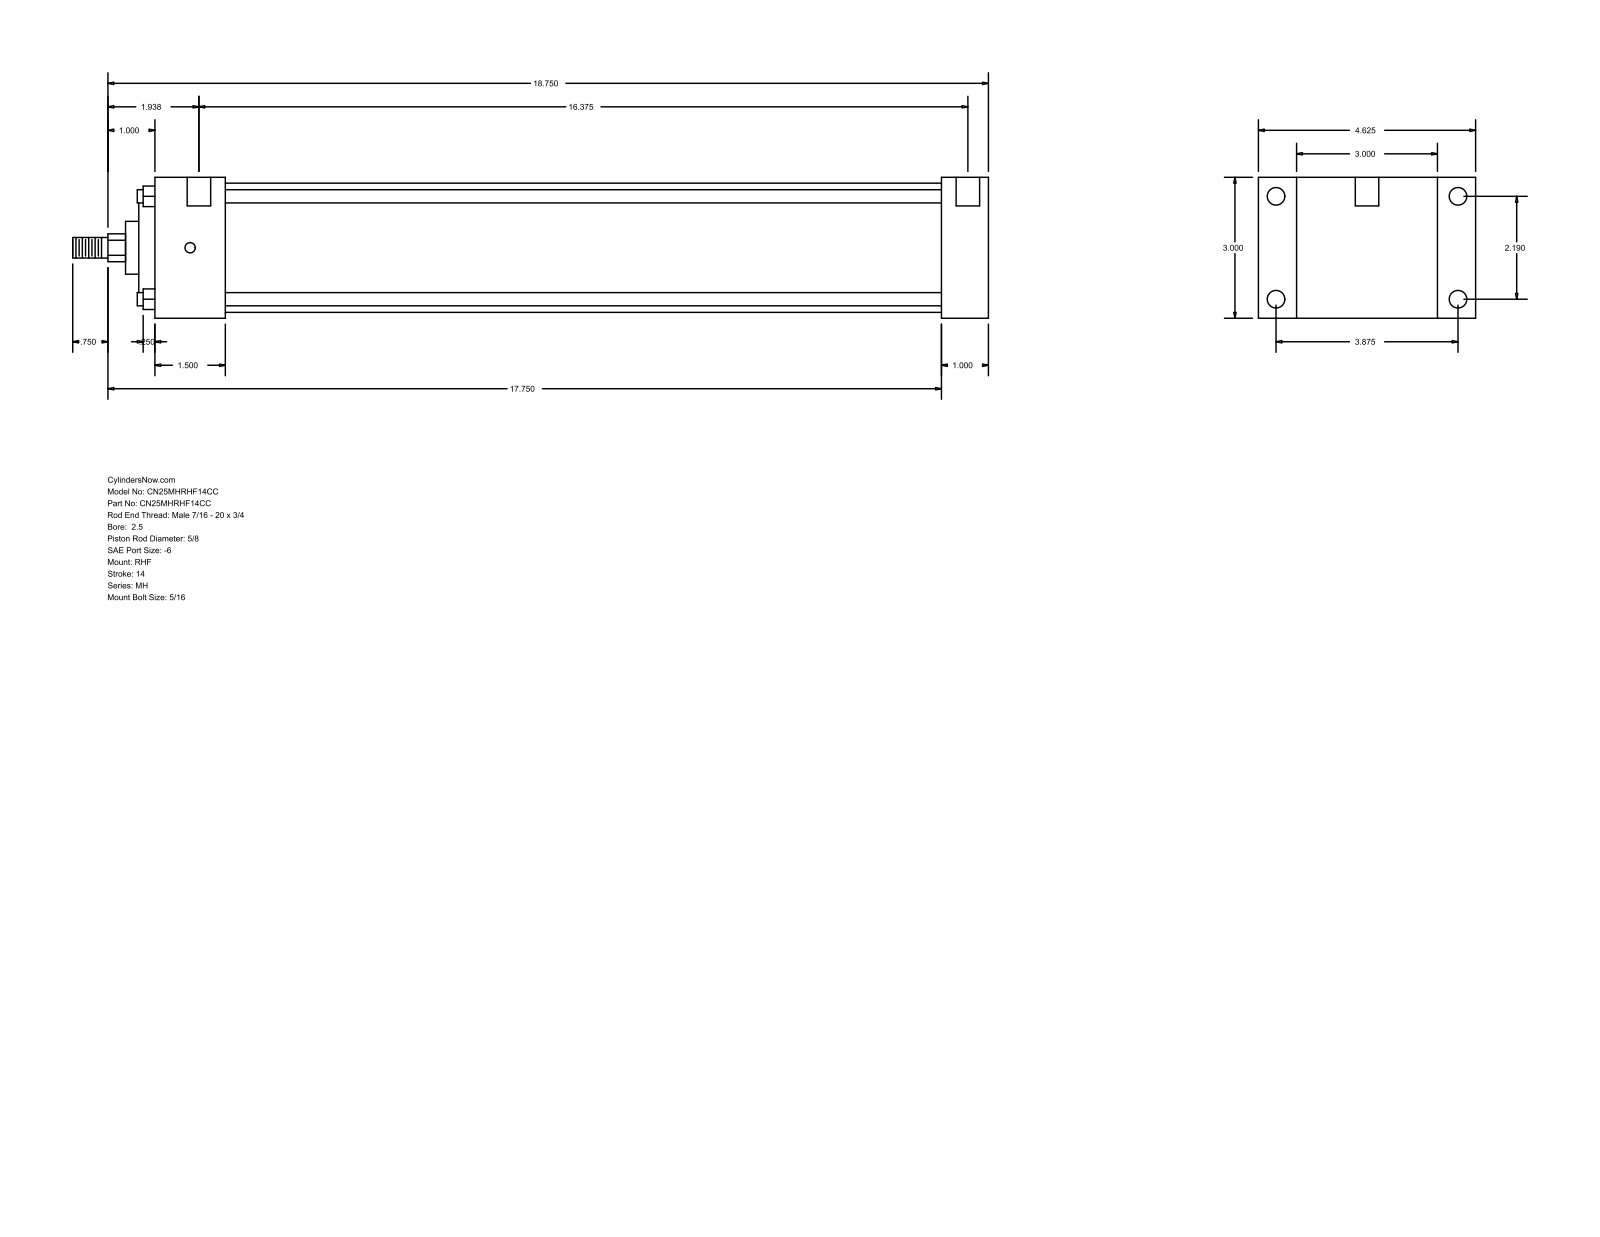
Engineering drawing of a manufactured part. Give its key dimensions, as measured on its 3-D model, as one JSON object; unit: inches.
{"part_name": "MH_RHF__0250_0.625", "step_written_by": "GSSL Pune (CONFIG_CONTROL_DESIGN)", "units": "inches", "bodies": {"solids": 0, "faces": 90, "planar": 61, "cylindrical": 29, "other": 0}, "overall_size": [19.5, 4.625, 3], "round_holes": [[0.219, 4], [0.375, 4], [0.5, 2]], "round_bosses_or_shafts": [[0.281, 4], [2.75, 1], [2.187, 1], [1.125, 1], [0.625, 1], [0.437, 1]], "partial_cylinders_radius": [[0.297, 1]], "face_to_face_distances": [3, 1, 0.813, 3.813, 17.75, 16.75, 1.5, 4.625, 15.25, 16.25], "hole_center_spacings": [2.19, 3.875, 4.451, 16.687, 0.125, 0.187, 16.375, 16.5]}
